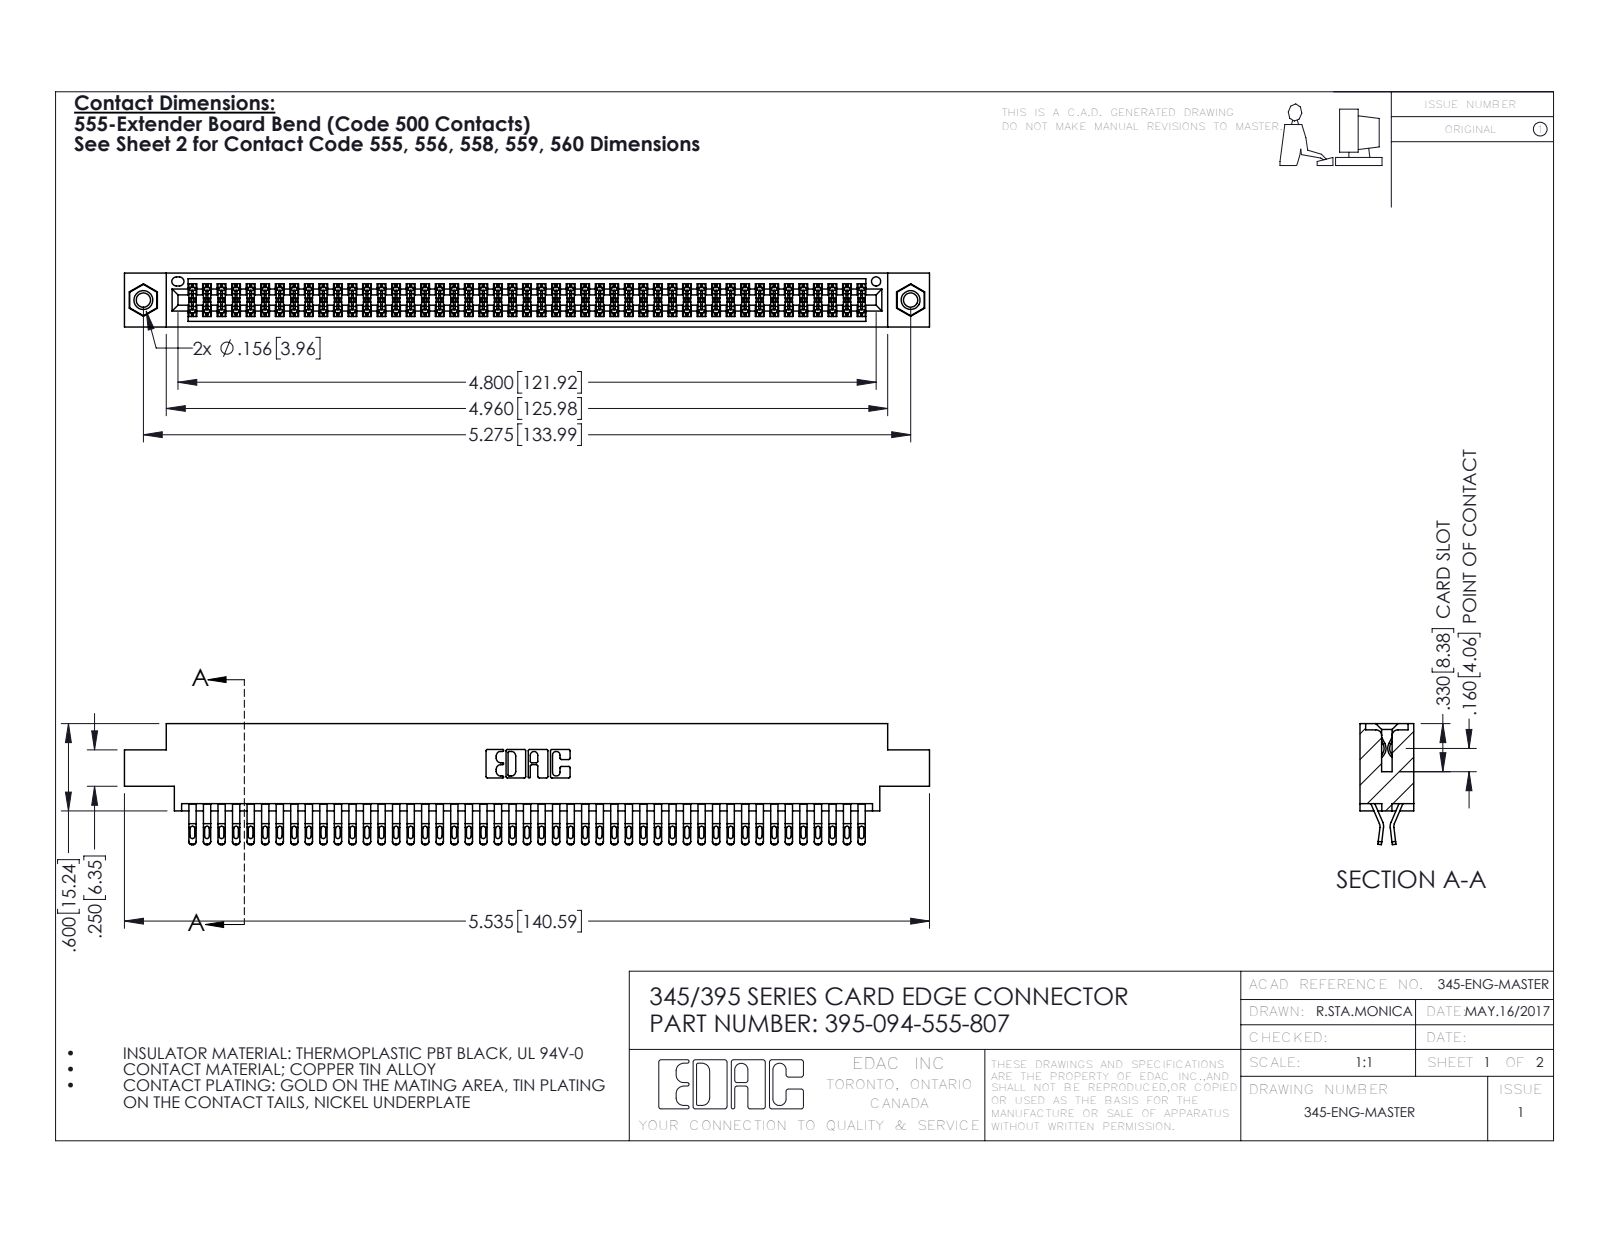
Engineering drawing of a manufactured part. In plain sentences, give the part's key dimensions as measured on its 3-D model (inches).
The part is named "395-094-555-807; 345-250-001_345-250-005-103; 345-292-001_555 Tail; 345 Part_0.170 Offset - 0.156 Dia-TI". Its 3-D file was written by "SolidWorks 2016 (CONFIG_CONTROL_DESIGN)". It is 97 solids with 5454 faces: 3030 planar, 2408 cylindrical and 16 other. Overall it measures 5.535 by 0.832 by 0.37 inches. Its volume is 0.845 cubic inches and its surface area 33.62 square inches. Round holes: 2 of diameter 0.098, 2 of diameter 0.125, 2 of diameter 0.156, 1 of diameter 0.064. Round bosses or shafts: 2 of diameter 0.155. Partial cylindrical surfaces (rounded edges, fillets, slot ends): 235 of radius 0.016, 188 of radius 0.02, 141 of radius 0.006, 22 of radius 0.01, 6 of radius 0.007, 6 of radius 0.031, 3 of radius 0.026, 2 of radius 0.01. The main face-to-face distances are 0.072, 0.298, 0.37, 0.025, 0.2, 0.098, 0.272, 0.225, 0.175, 0.149. The hole center spacings are 0.27, 5.039, 5.275.
